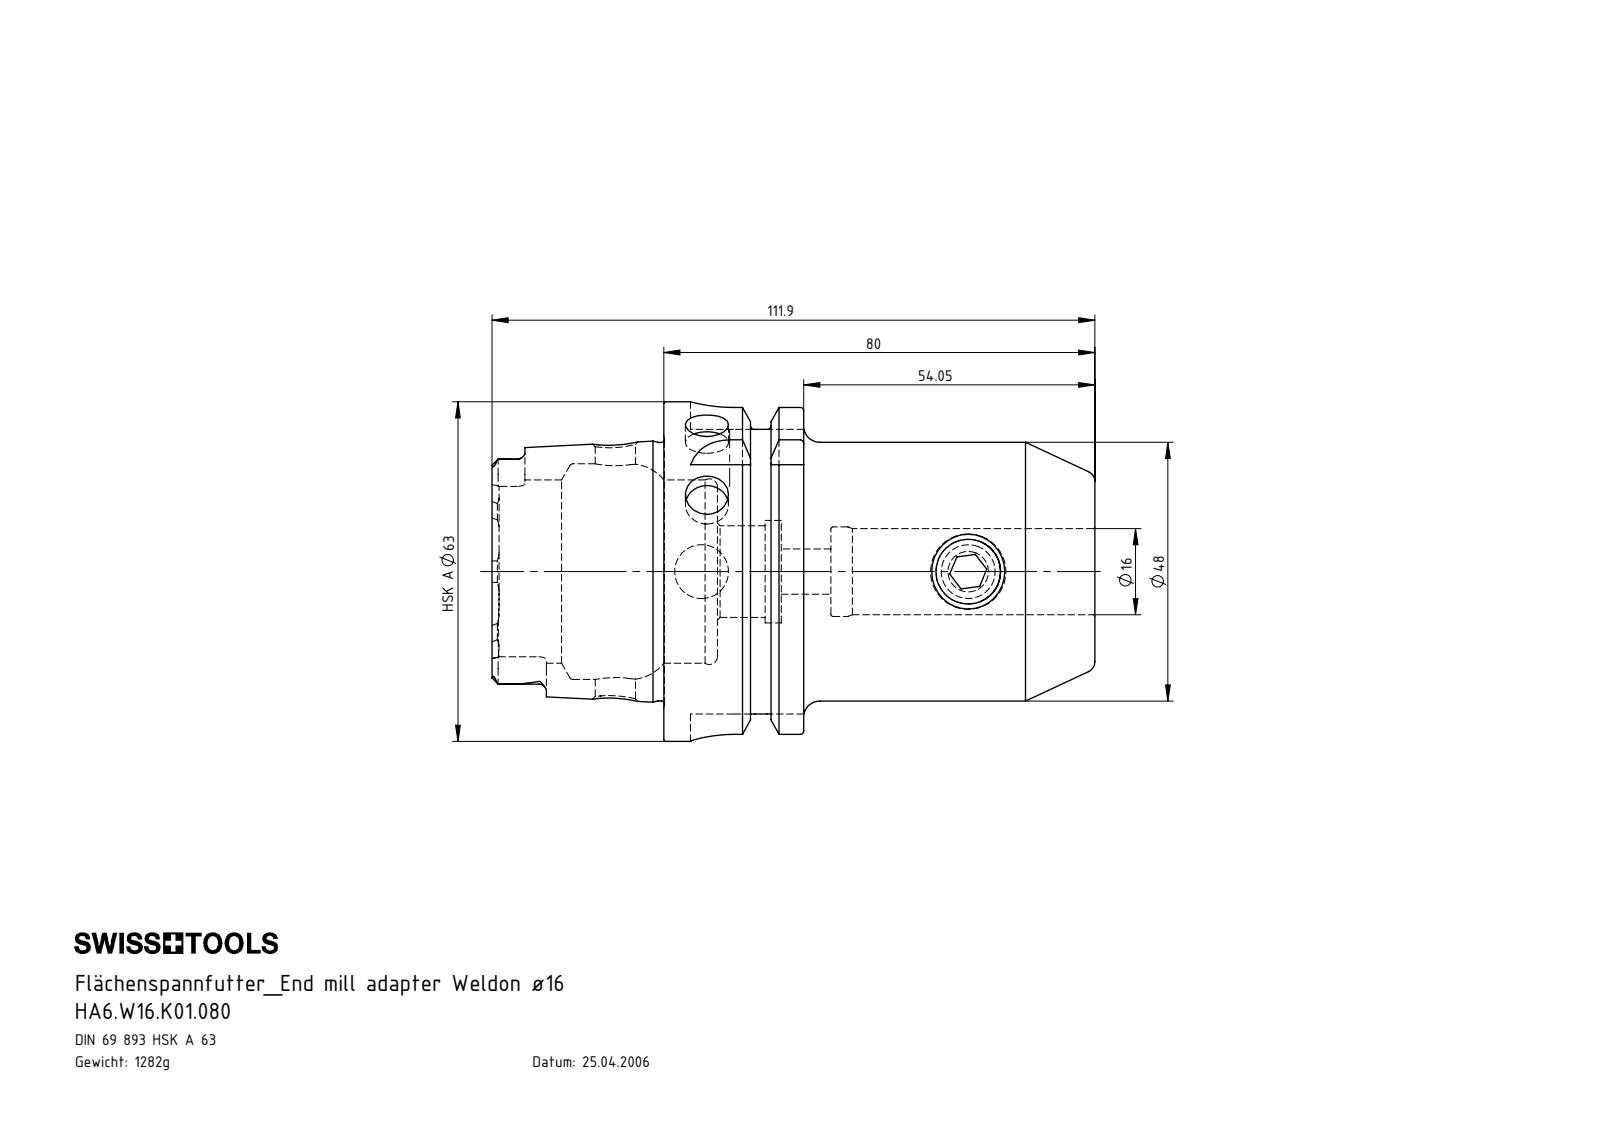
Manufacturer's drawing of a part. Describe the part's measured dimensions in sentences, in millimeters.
The part is named "HA6-W16.K01.080; W16-ER1.001.016; HA6-W16.K01.080_B_Fertigbearbeitung". Its 3-D file was written by "SolidWorks 2012 (AUTOMOTIVE_DESIGN)". It is 2 solids with 209 faces: 59 planar, 57 cylindrical and 93 other. Overall it measures 111.9 by 63 by 63 millimeters. Its volume is 163 263 cubic millimeters and its surface area 33 682 square millimeters. Round holes: 2 of diameter 8, 1 of diameter 7.5, 1 of diameter 8.4, 1 of diameter 10, 1 of diameter 12, 1 of diameter 16, 1 of diameter 16.6, 1 of diameter 17, 1 of diameter 19, 1 of diameter 34, 1 of diameter 40. Round bosses or shafts: 1 of diameter 63, 1 of diameter 54.95, 1 of diameter 48, 1 of diameter 47.94, 1 of diameter 14. Partial cylindrical surfaces (rounded edges, fillets, slot ends): 6 of radius 1.4, 4 of radius 2.88, 4 of radius 8. The main face-to-face distances are 80, 25.95, 54.05, 16, 9.95, 70.05, 52.8, 31.9, 41.85, 57.85. The hole center spacings are 49.5.
